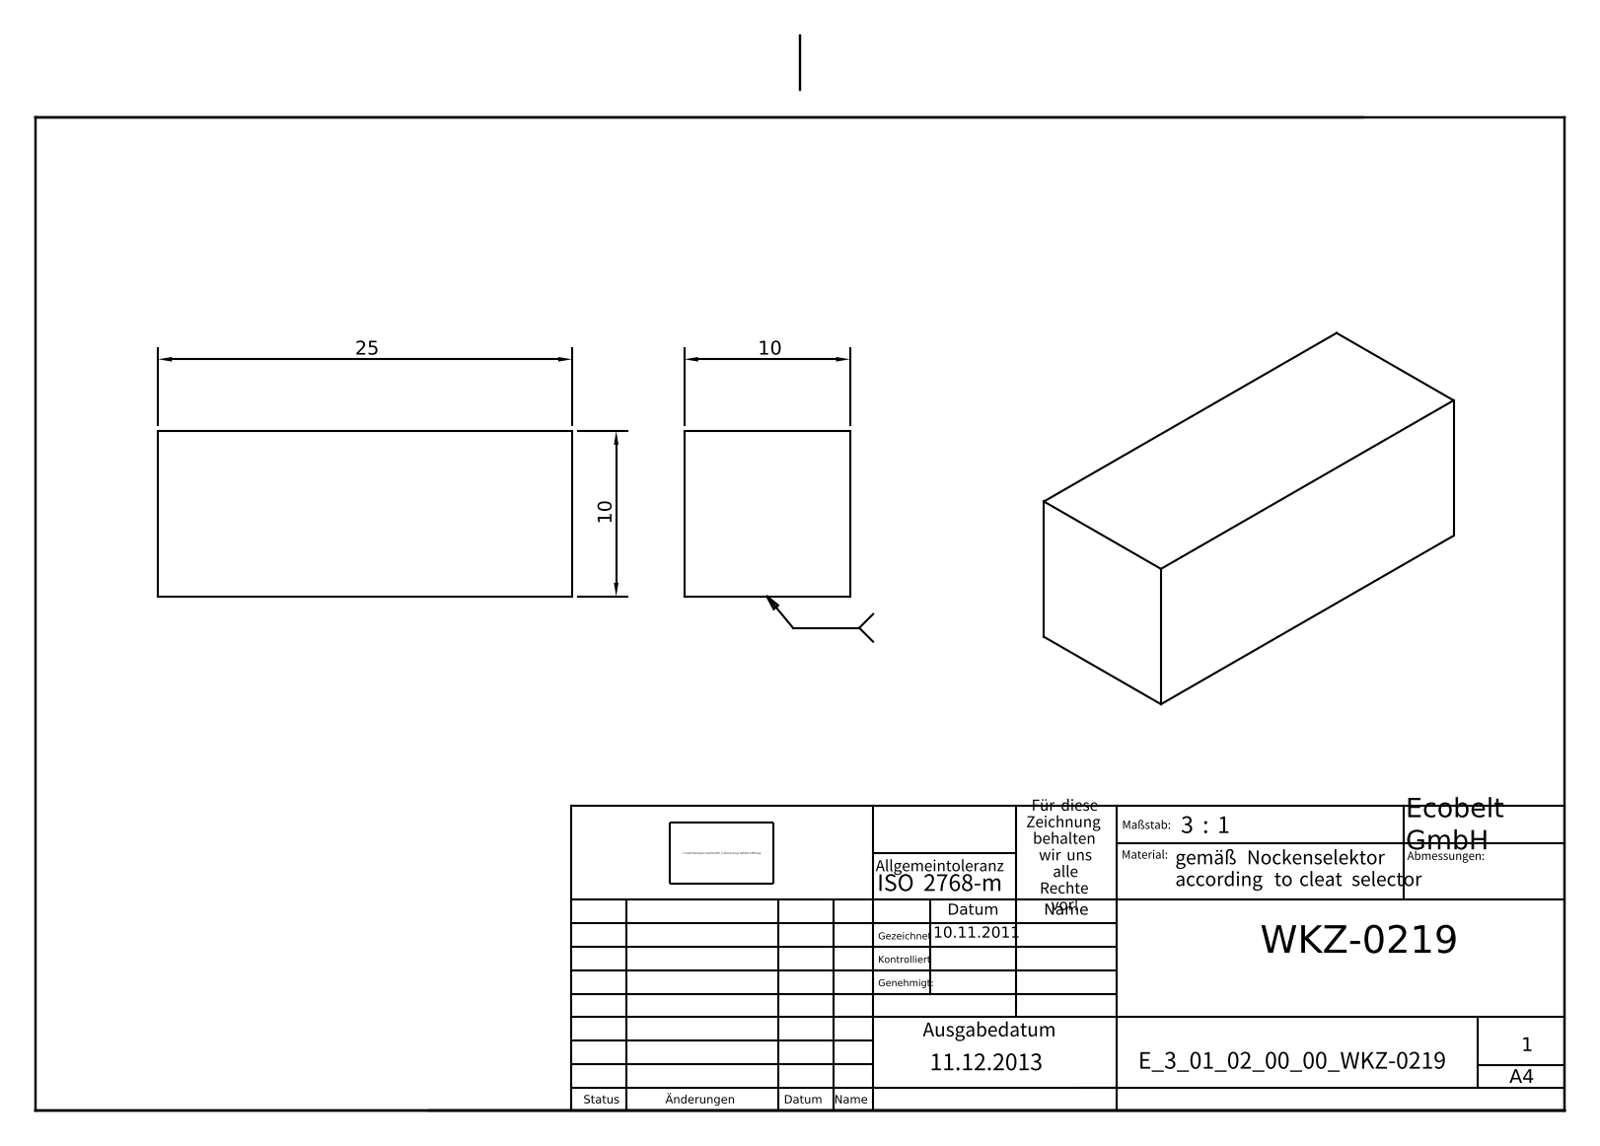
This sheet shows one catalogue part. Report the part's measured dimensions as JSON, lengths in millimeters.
{"part_name": "E_3_01_02_00_00_WKZ-0219", "step_written_by": "Autodesk Inventor 2021 (AUTOMOTIVE_DESIGN)", "units": "millimeters", "bodies": {"solids": 1, "faces": 6, "planar": 6, "cylindrical": 0, "other": 0}, "overall_size": [25, 10, 10], "volume_mm3": 2500, "surface_area_mm2": 1200, "face_to_face_distances": [10, 25]}
